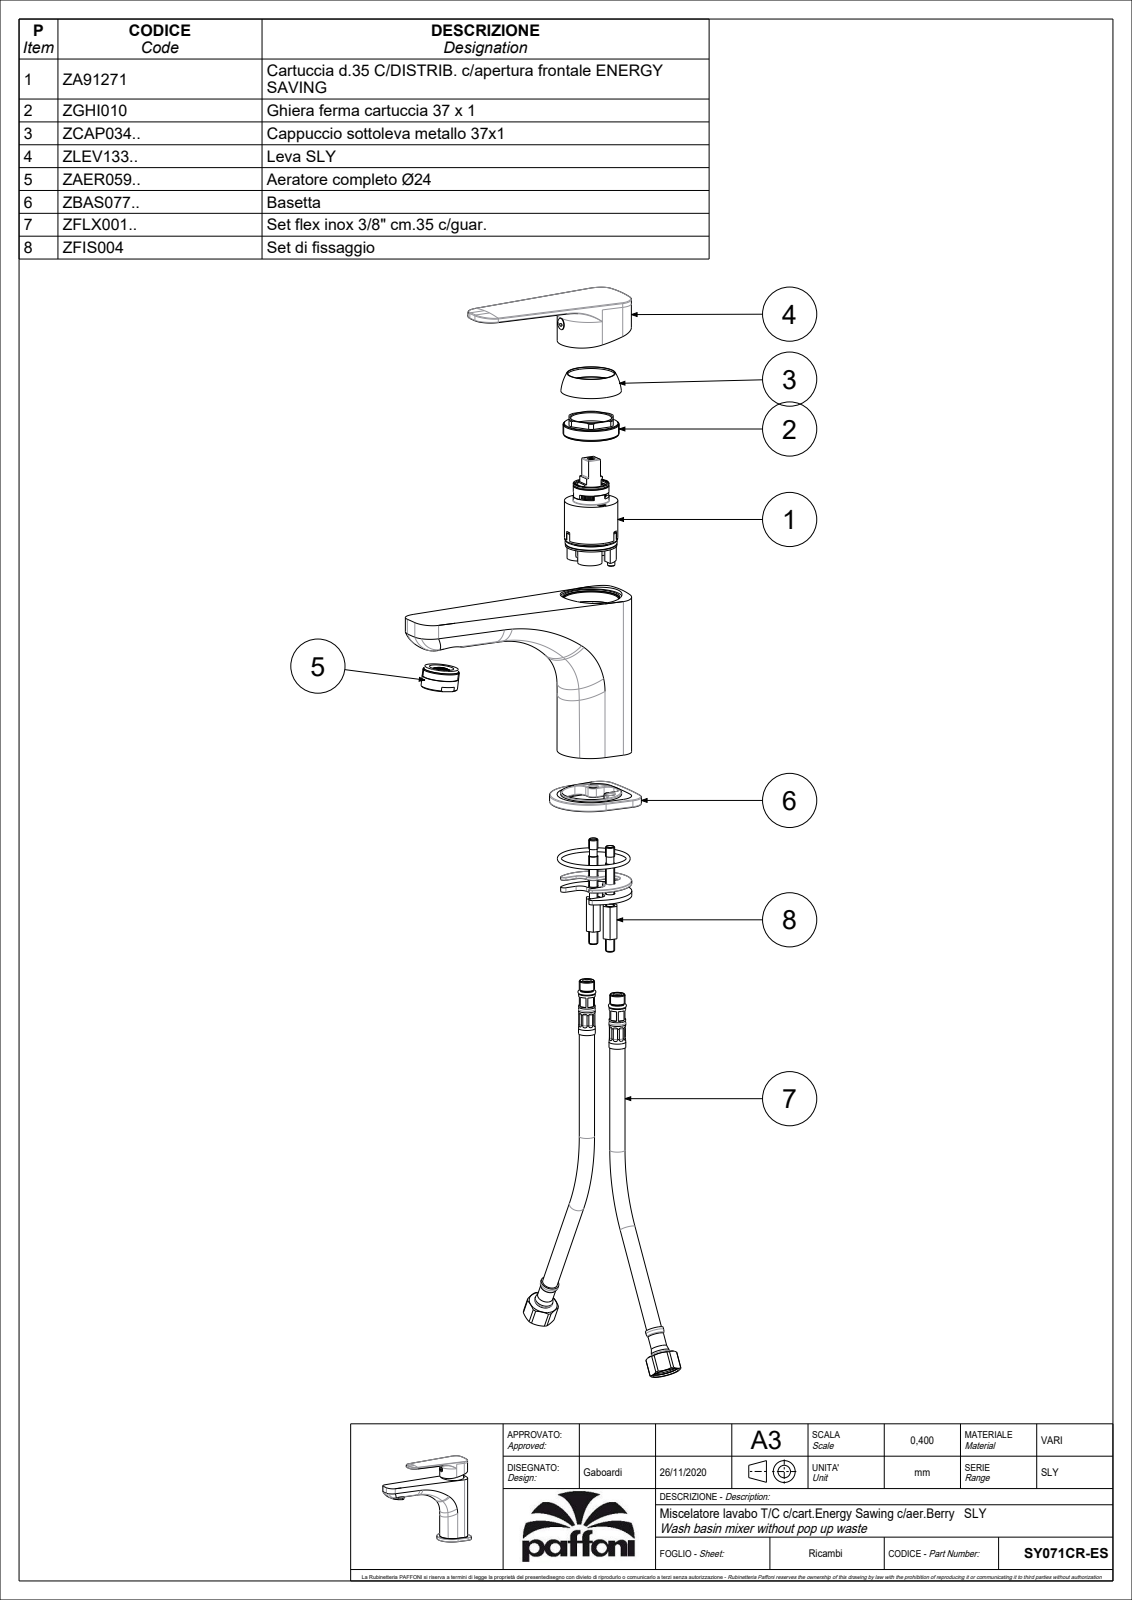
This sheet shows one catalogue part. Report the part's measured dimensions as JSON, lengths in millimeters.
{"part_name": "SY071CR", "step_written_by": "CREO PARAMETRIC BY PTC INC, 2020044 (CONFIG_CONTROL_DESIGN)", "units": "millimeters", "bodies": {"solids": 2, "faces": 2771, "planar": 2066, "cylindrical": 384, "other": 321}, "overall_size": [163.5, 142.8, 53.82], "volume_mm3": 184520, "surface_area_mm2": 108810, "round_holes": [[9, 5], [5, 3], [12, 3], [4, 2], [6.2, 2], [7, 2], [8, 2], [11, 2], [16, 2], [3, 1], [3.3, 1], [4.5, 1]], "round_bosses_or_shafts": [[10, 2], [42, 1], [40, 1], [35, 1], [34.8, 1], [33.8, 1], [32.2, 1], [29.8, 1]], "partial_cylinders_radius": [[0.5, 54], [1.5, 14], [0.15, 11], [0.3, 9], [10, 6], [1, 4], [5, 4], [7, 4]], "face_to_face_distances": [3.7, 3, 9.5, 5, 15, 0.5, 2, 21.5, 24.5, 59.5], "hole_center_spacings": [13.6, 0.5, 0.71, 1.12, 8.51, 8.6, 9.01, 11.18]}
